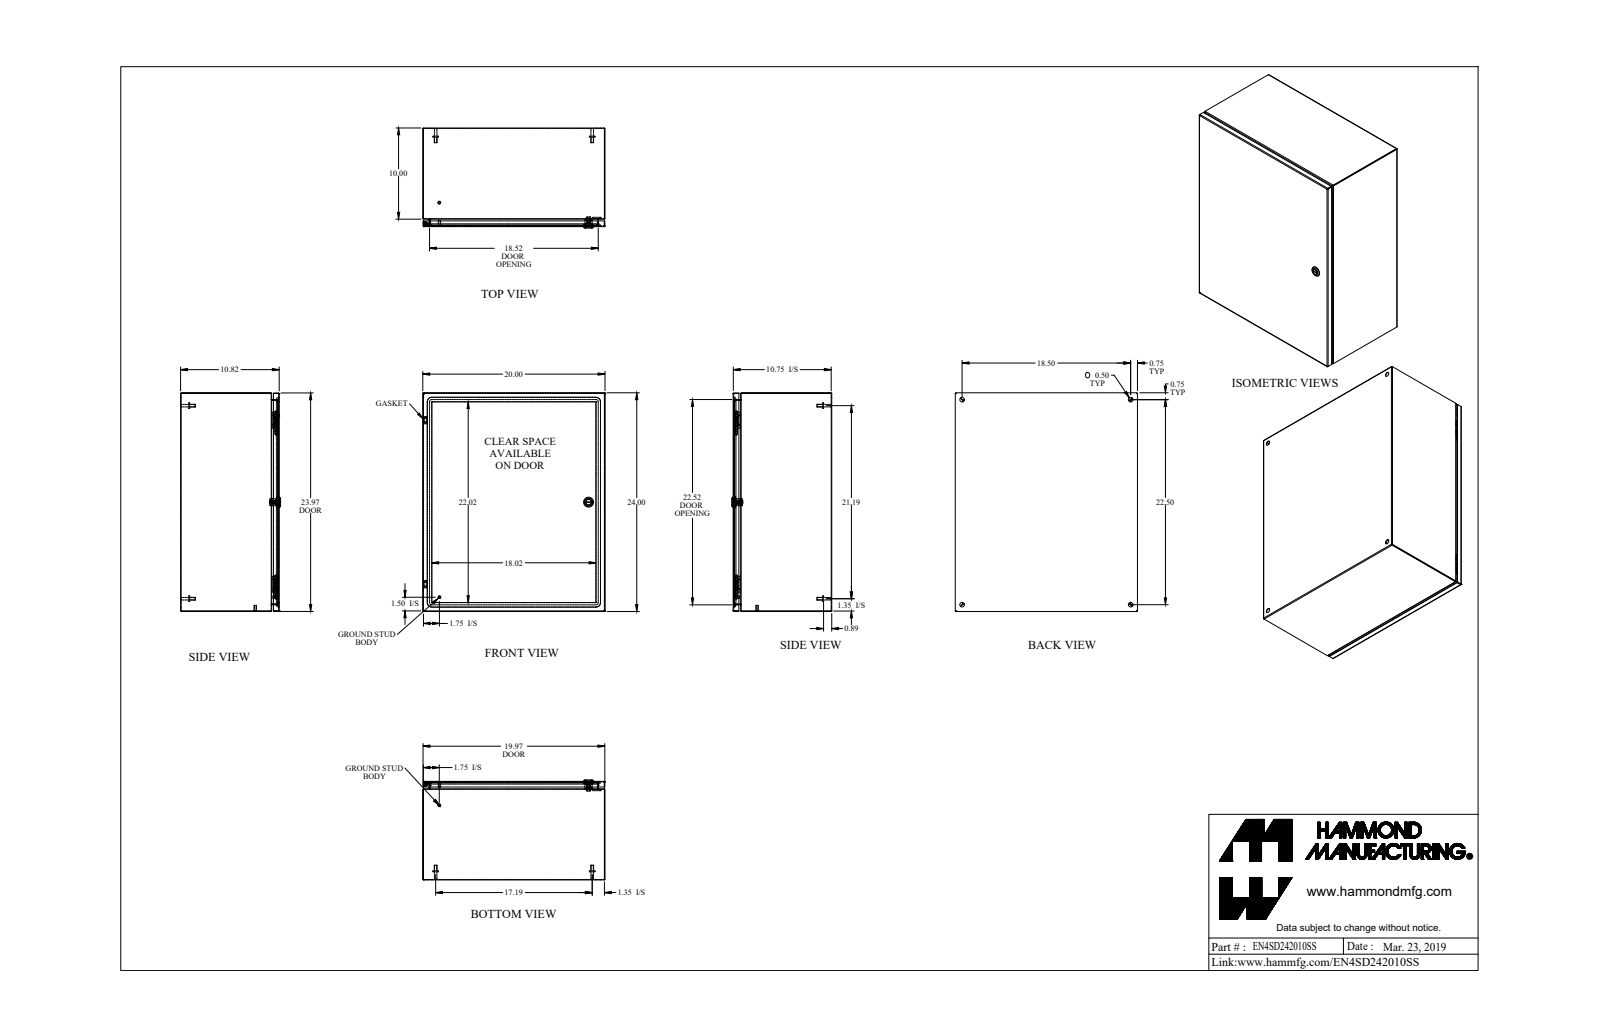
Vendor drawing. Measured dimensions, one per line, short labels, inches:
name: EN4SD242010SS_Default
written by: SolidWorks 2019 (CONFIG_CONTROL_DESIGN)
unit: in
bodies: 22 solids, 657 faces (303 planar, 212 cylindrical, 142 other)
size: 24 × 20 × 10.982
volume: 123.2 in³; area: 4 219 in²
holes: 5× ⌀0.5, 1× ⌀0.172, 1× ⌀0.197, 1× ⌀0.24, 1× ⌀0.242, 1× ⌀0.387, 1× ⌀0.63, 1× ⌀0.768
bosses: 6× ⌀0.313, 5× ⌀0.625, 4× ⌀0.275, 2× ⌀0.25, 1× ⌀1.1, 1× ⌀0.785, 1× ⌀0.525, 1× ⌀0.455
rounds: 21× R0.029, 21× R0.086, 12× R0.188, 4× R0.006, 4× R0.062, 4× R0.25, 4× R0.499, 2× R0.125
face distances: 0.057, 10.765, 10.708, 10.822, 19.943, 23.943, 19.886, 20, 23.886, 24
hole spacings: 11.3, 18.5, 20.754, 22.5, 29.129
